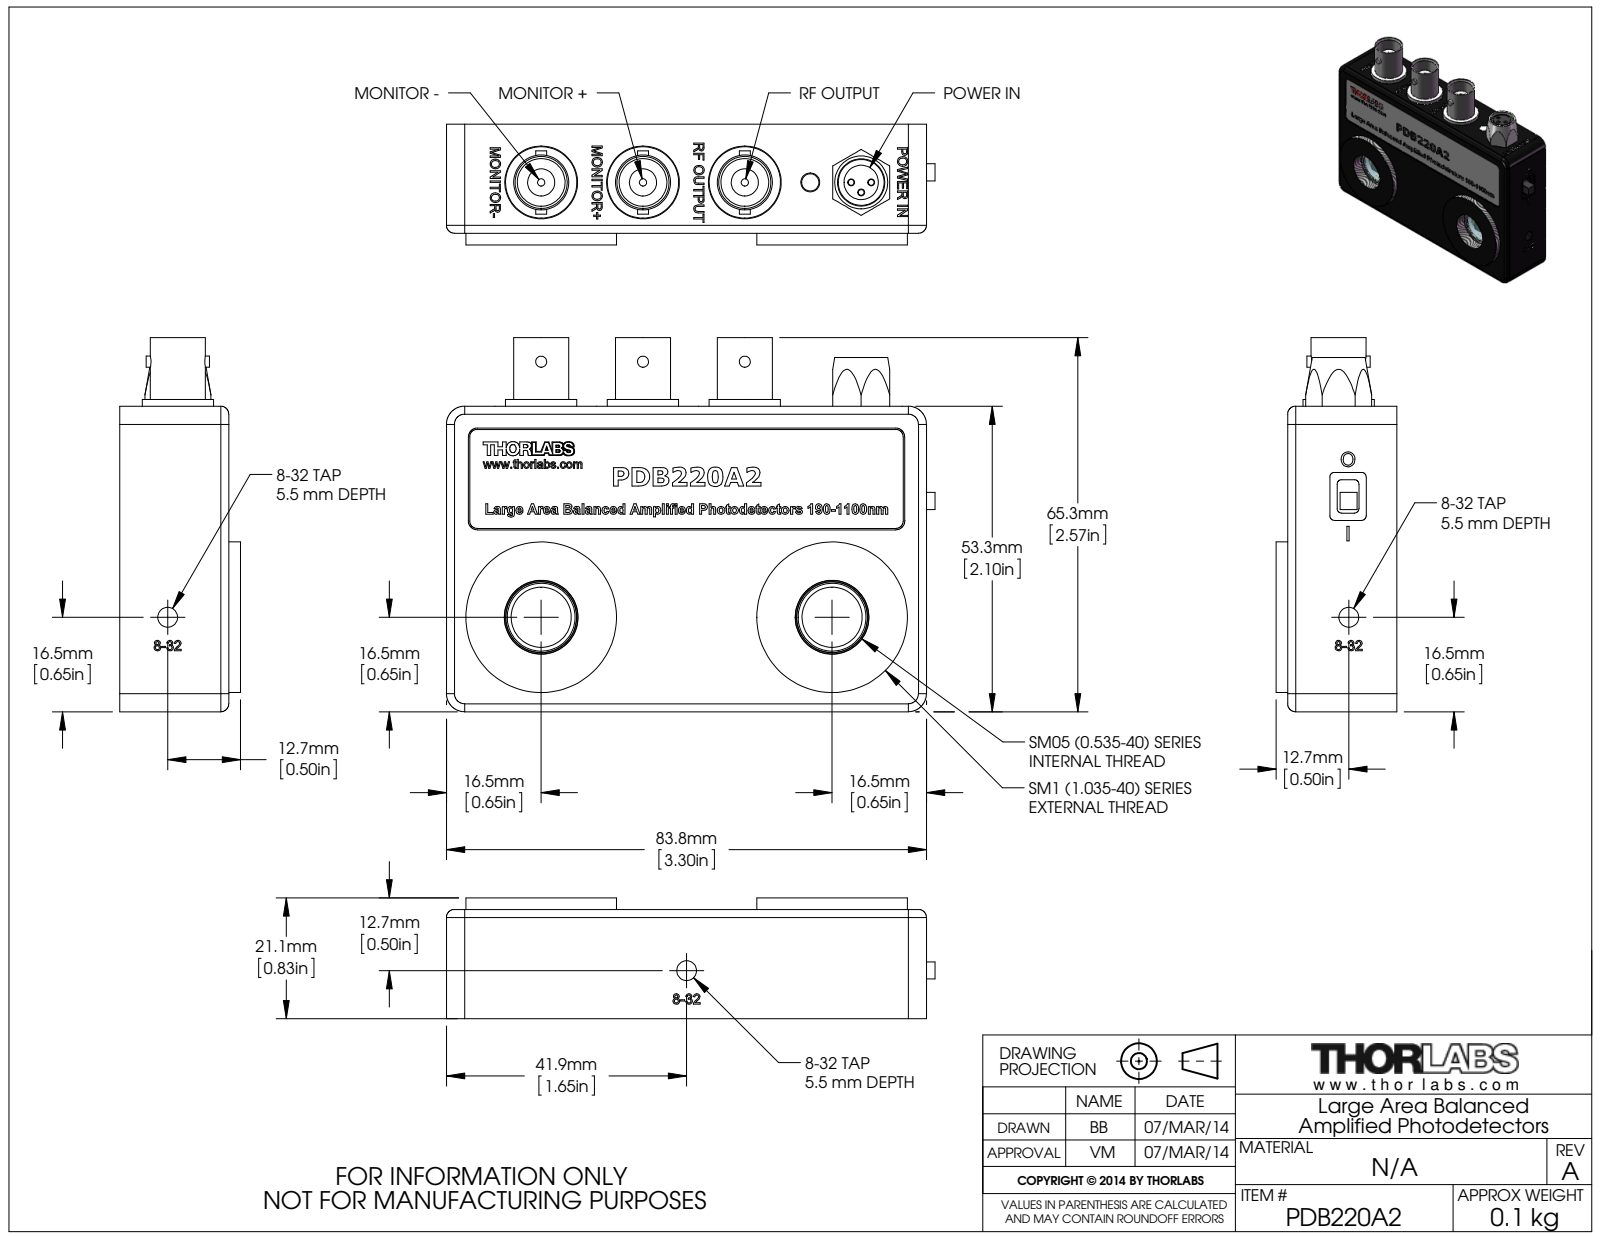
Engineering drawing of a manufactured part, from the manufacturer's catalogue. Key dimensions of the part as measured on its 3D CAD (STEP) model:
Part name (STEP PRODUCT): MTN003813-E0W
STEP written by: SolidWorks 2013 (AUTOMOTIVE_DESIGN)
Units: millimetres
Bodies: 37 solids, 2892 faces (1666 planar, 318 cylindrical, 908 other)
Overall size (bounding box): 85.28 × 65.3 × 21.08
Volume: 33 231 mm³ · Surface area: 38 585 mm²
Round holes (diameter × count): ⌀1.6 ×7, ⌀2.4 ×4, ⌀3.17 ×4, ⌀1 ×3, ⌀1.27 ×3, ⌀1.32 ×3, ⌀8.33 ×3, ⌀11.13 ×3, ⌀12.7 ×3, ⌀3.45 ×2, ⌀10.5 ×2, ⌀11.85 ×2
Round bosses / shafts (diameter × count): ⌀0.51 ×6, ⌀3 ×5, ⌀12.45 ×3, ⌀10.92 ×3, ⌀9.6 ×3, ⌀9.4 ×3, ⌀8.2 ×3, ⌀5.33 ×3
Partial cylindrical surfaces — rounded edges, fillets, slot ends (radius × count): R3.17 ×31, R3.3 ×14, R0.79 ×8, R2.41 ×8, R1.27 ×4, R1.4 ×4, R1.59 ×4, R2.79 ×4
Main face-to-face distances: 1.59, 2.54, 1.27, 17.27, 15.68, 18.54, 16.95, 1.78, 0.51, 19.05
Hole centre spacings: 1.75, 2.47, 15.21, 17.78, 22.43, 22.69, 26.18, 34.97
